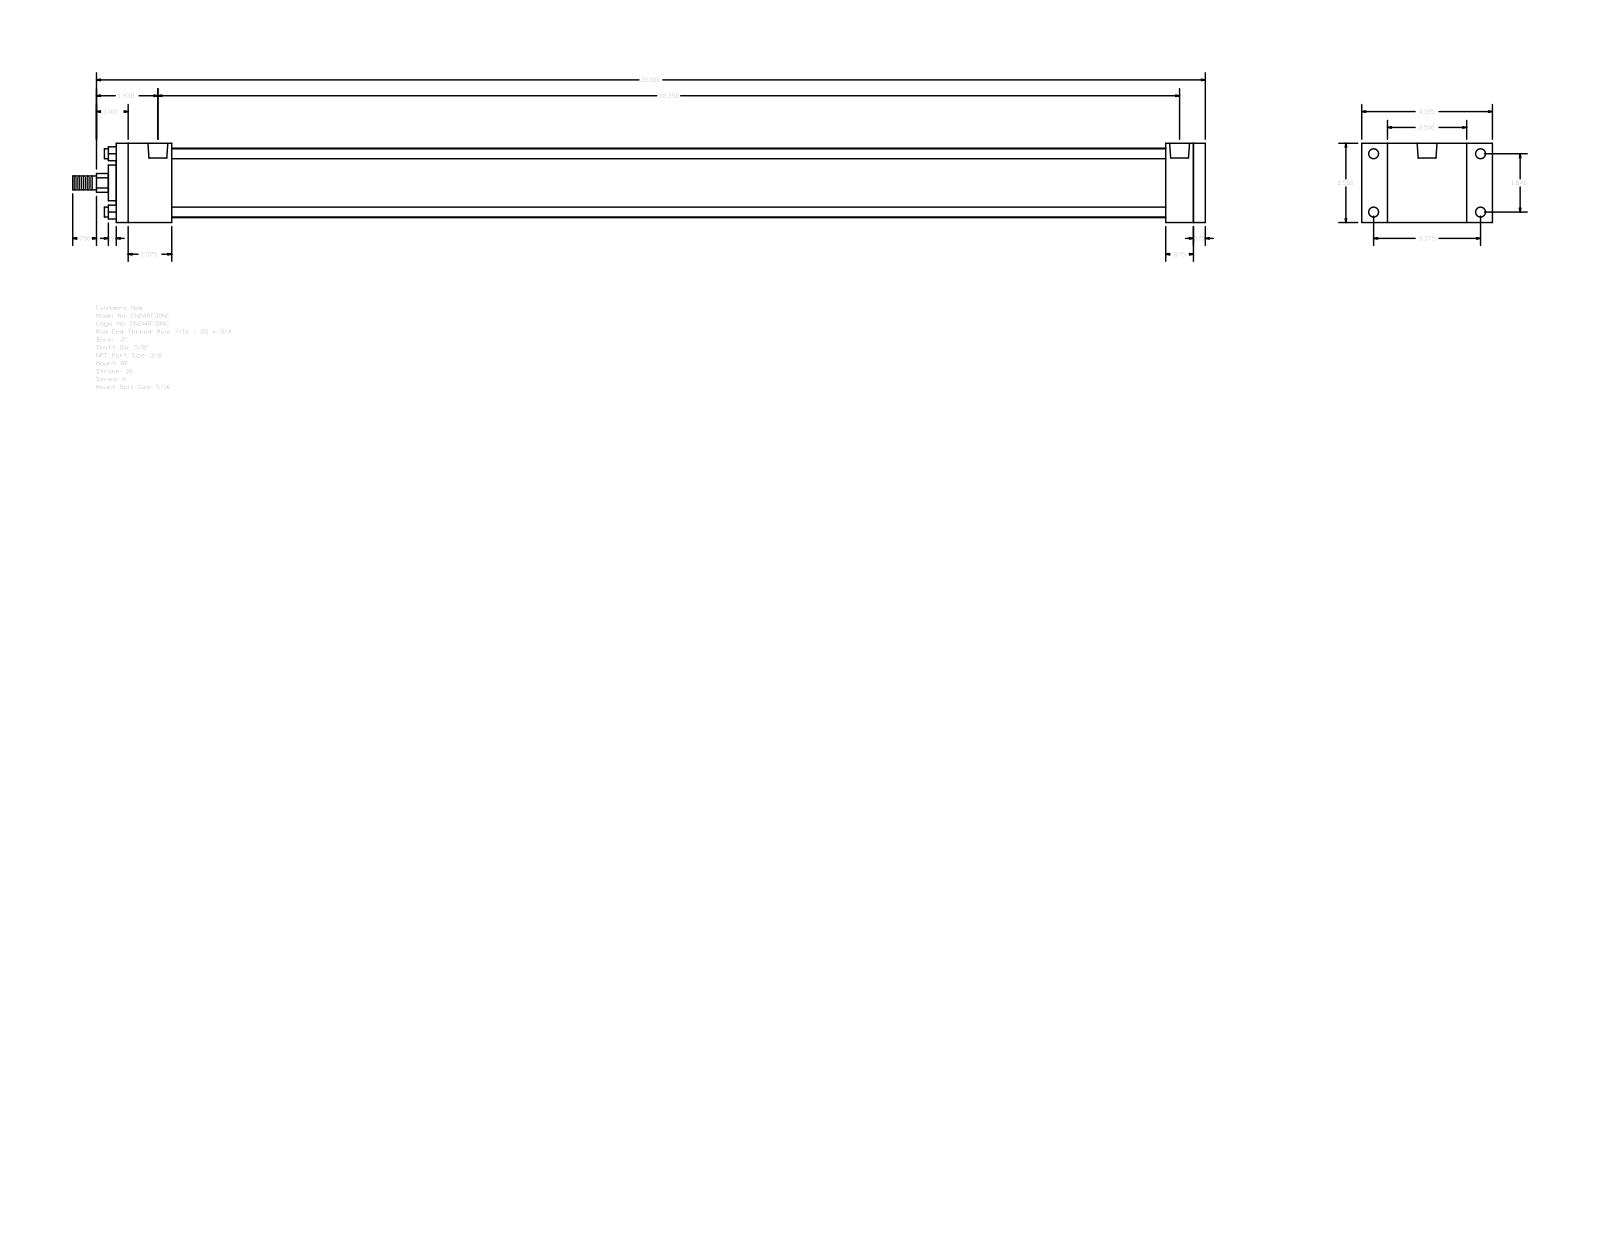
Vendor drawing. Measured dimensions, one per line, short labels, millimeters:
name: A_RF__0200_0.625
written by: GSSL Pune (CONFIG_CONTROL_DESIGN)
unit: mm
bodies: 0 solids, 92 faces (64 planar, 28 cylindrical, 0 other)
size: 908.05 × 104.78 × 63.5
holes: 4× ⌀5.56, 4× ⌀7.94, 2× ⌀15.93
bosses: 4× ⌀7.94, 1× ⌀55.63, 1× ⌀28.57, 1× ⌀15.88, 1× ⌀11.11
rounds: 1× R7.54
face distances: 63.5, 873.12, 863.6, 9.52, 44.45, 819.15, 828.67, 841.37, 796.92, 22.23
hole spacings: 46.74, 85.72, 97.63, 811.2, 3.97, 3.98, 815.17, 815.18
